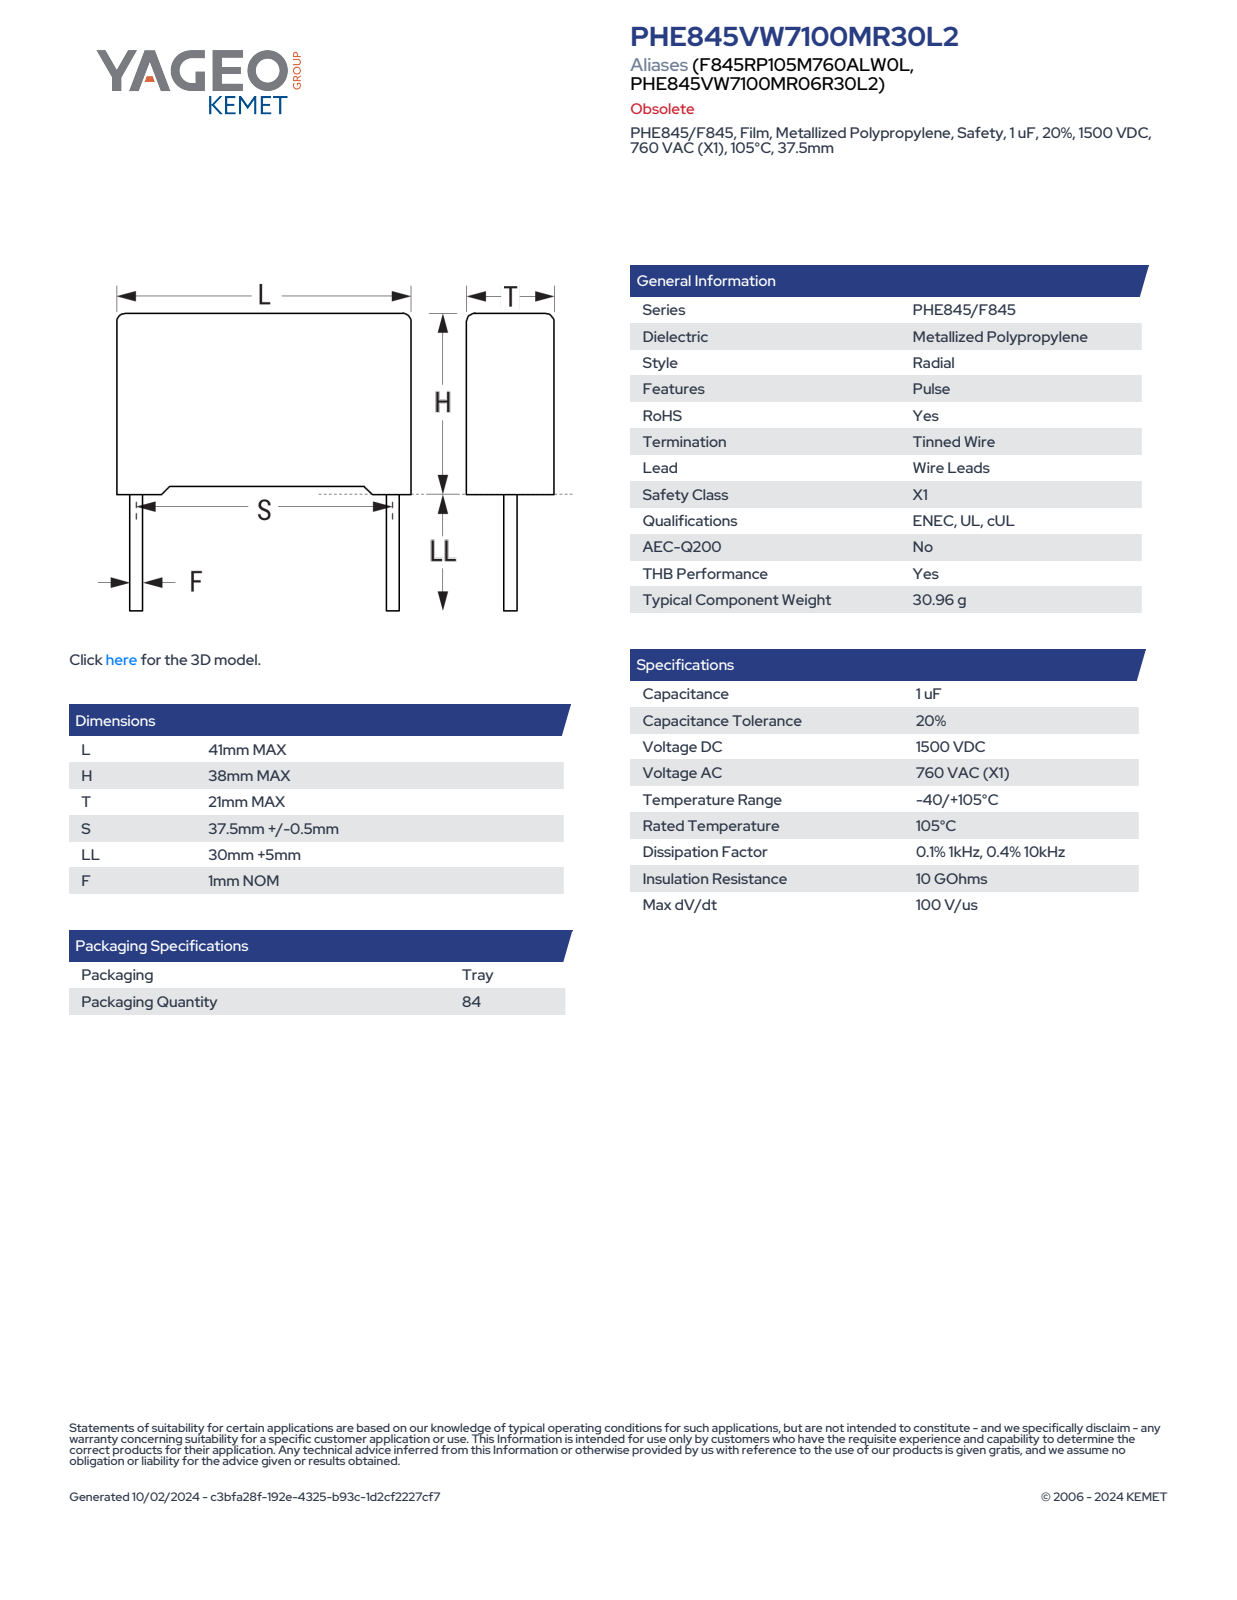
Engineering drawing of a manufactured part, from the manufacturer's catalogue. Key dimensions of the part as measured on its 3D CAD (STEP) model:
Part name (STEP PRODUCT): CFR_RB2_41X38X21_L41H38T21S37.5LL35F1.05
STEP written by: SolidWorks 2021 (AUTOMOTIVE_DESIGN)
Units: millimetres
Bodies: 4 solids, 87 faces (79 planar, 8 cylindrical, 0 other)
Overall size (bounding box): 73 × 41 × 21
Volume: 31 795 mm³ · Surface area: 6 726 mm²
Round bosses / shafts (diameter × count): ⌀1.05 ×2
Partial cylindrical surfaces — rounded edges, fillets, slot ends (radius × count): R0.5 ×4
Main face-to-face distances: 21, 41, 36.69, 0.56, 37.25, 0.75, 1.31, 38, 1.37, 21.01
